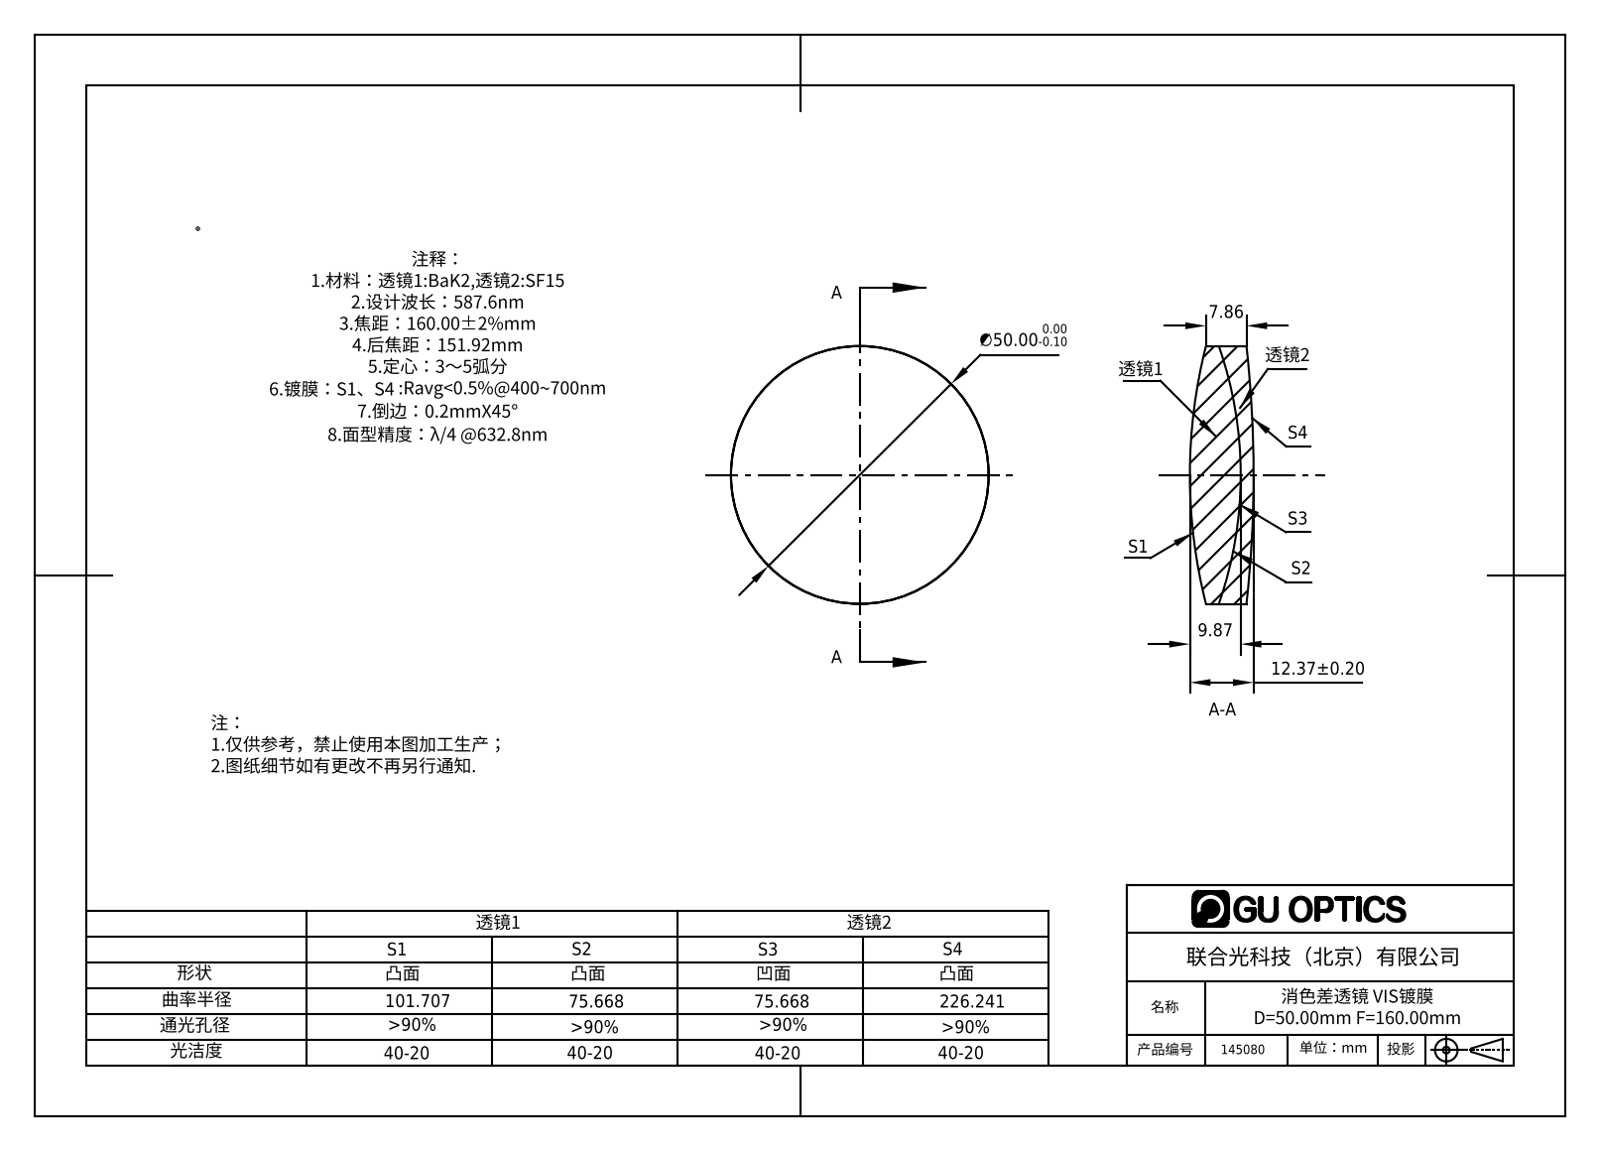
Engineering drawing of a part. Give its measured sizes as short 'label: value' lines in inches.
name: 145080
written by: SolidWorks 2016 (AUTOMOTIVE_DESIGN)
unit: in
bodies: 2 solids, 12 faces (0 planar, 4 cylindrical, 8 other)
size: 1.969 × 1.969 × 0.487
volume: 1.213 in³; area: 14.32 in²
bosses: 1× ⌀1.969
